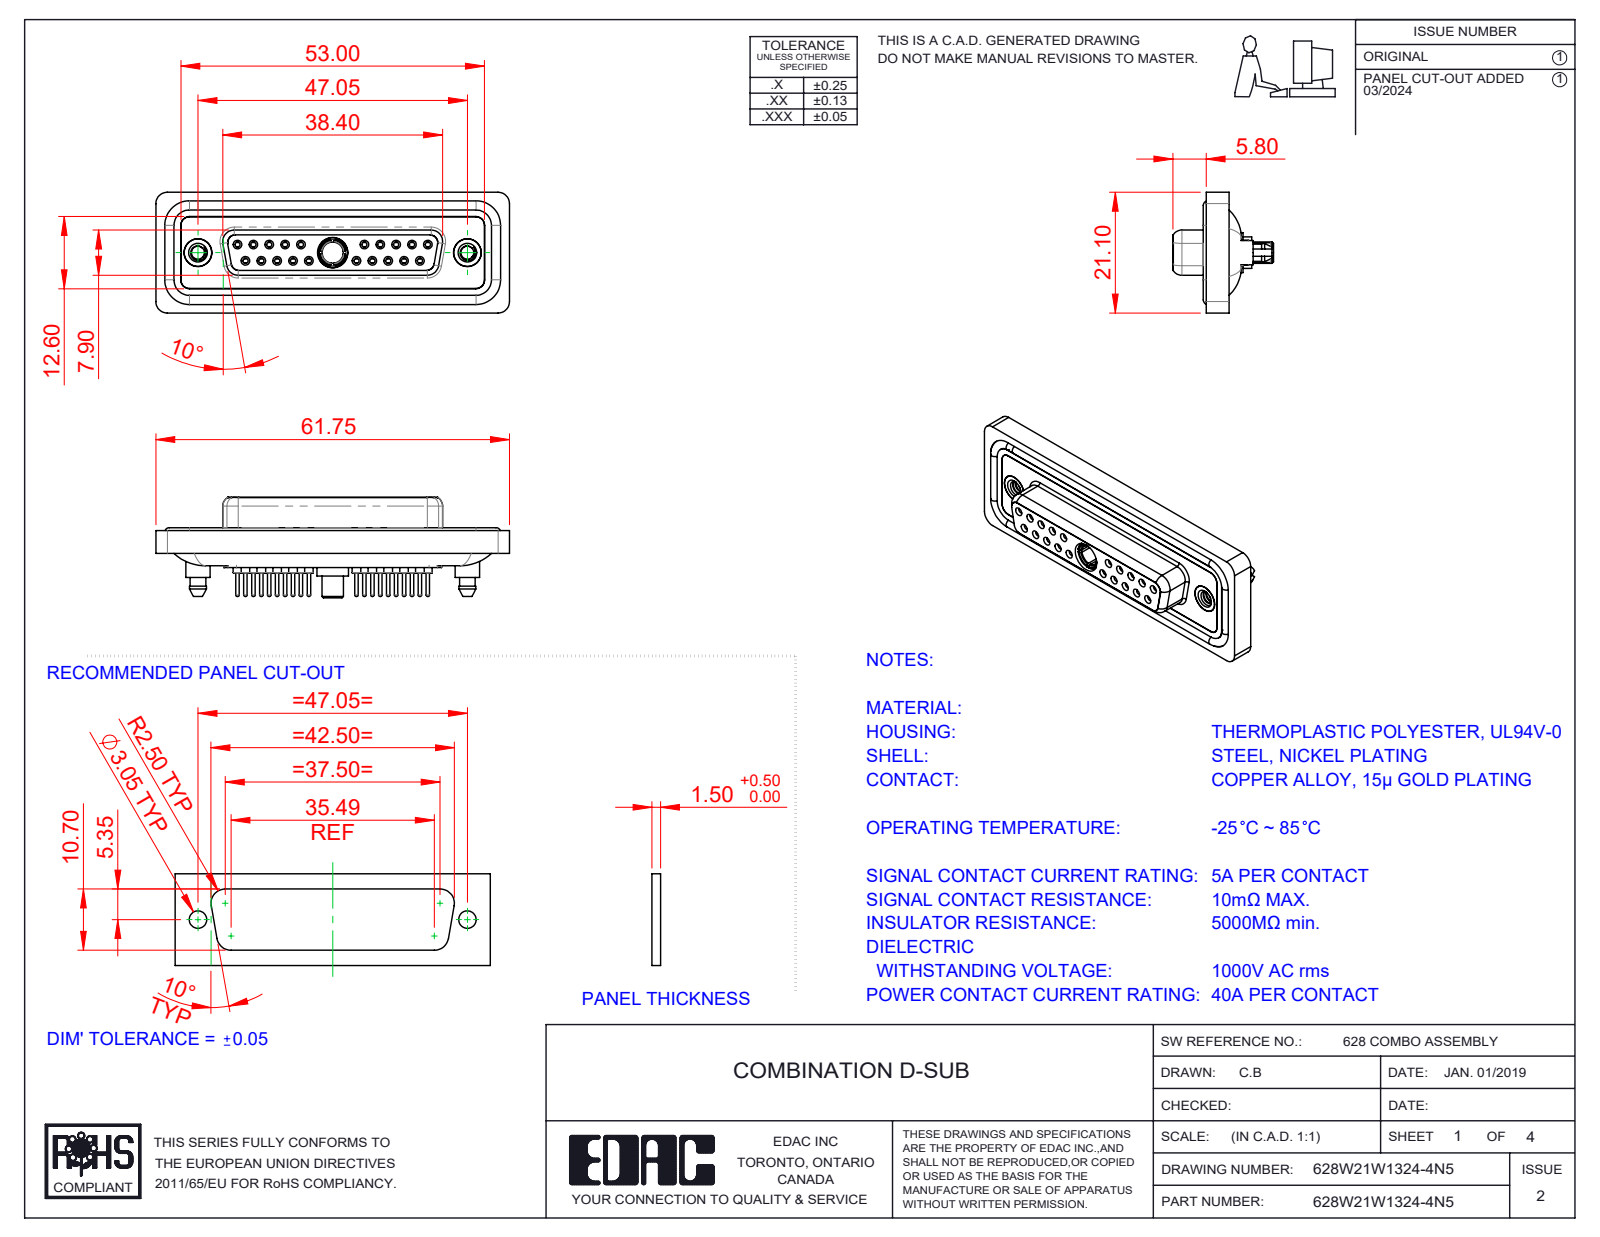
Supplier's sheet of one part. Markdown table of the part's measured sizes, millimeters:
| quantity | value |
| --- | --- |
| part name | 628W21W1324-4N5; 628Combo Threaded Boardlock_5; 628Combo Contact Row 1_24; 628Combo Contact Row 2_24 (+5 more) |
| STEP written by | SolidWorks 2023 (CONFIG_CONTROL_DESIGN) |
| units | millimeters |
| bodies | 29 solids, 1610 faces (450 planar, 623 cylindrical, 537 other) |
| overall size | 61.75 × 21.1 × 17.55 |
| volume | 8 526 mm³ |
| surface area | 14 346 mm² |
| round holes (diameter × count) | 0.9 × 20, 1.1 × 20, 1.5 × 20, 2 × 20, 1.6 × 10, 1.7 × 10, 4.85 × 3, 2.26 × 2, 4 × 2, 4.05 × 2, 5 × 2, 3.7 × 1 |
| round bosses / shafts (diameter × count) | 2.2 × 20, 0.6 × 20, 1.6 × 14, 5.4 × 2, 4.95 × 2, 4.8 × 2, 4.25 × 2, 5.5 × 1 |
| partial cylindrical surfaces (radius × count) | 1.5 × 24, 2 × 18, 1.6 × 10, 1.35 × 8, 0.25 × 4, 0.5 × 4, 0.6 × 4, 0.65 × 4 |
| main face-to-face distances | 0.4, 1.8, 7.45, 6.6, 5.65, 1.6, 0.5, 7.05, 2.9, 1.1 |
| hole center spacings | 3.16, 2.77, 5.54, 5.03, 8.31, 7.48, 16.62, 19.39 |
